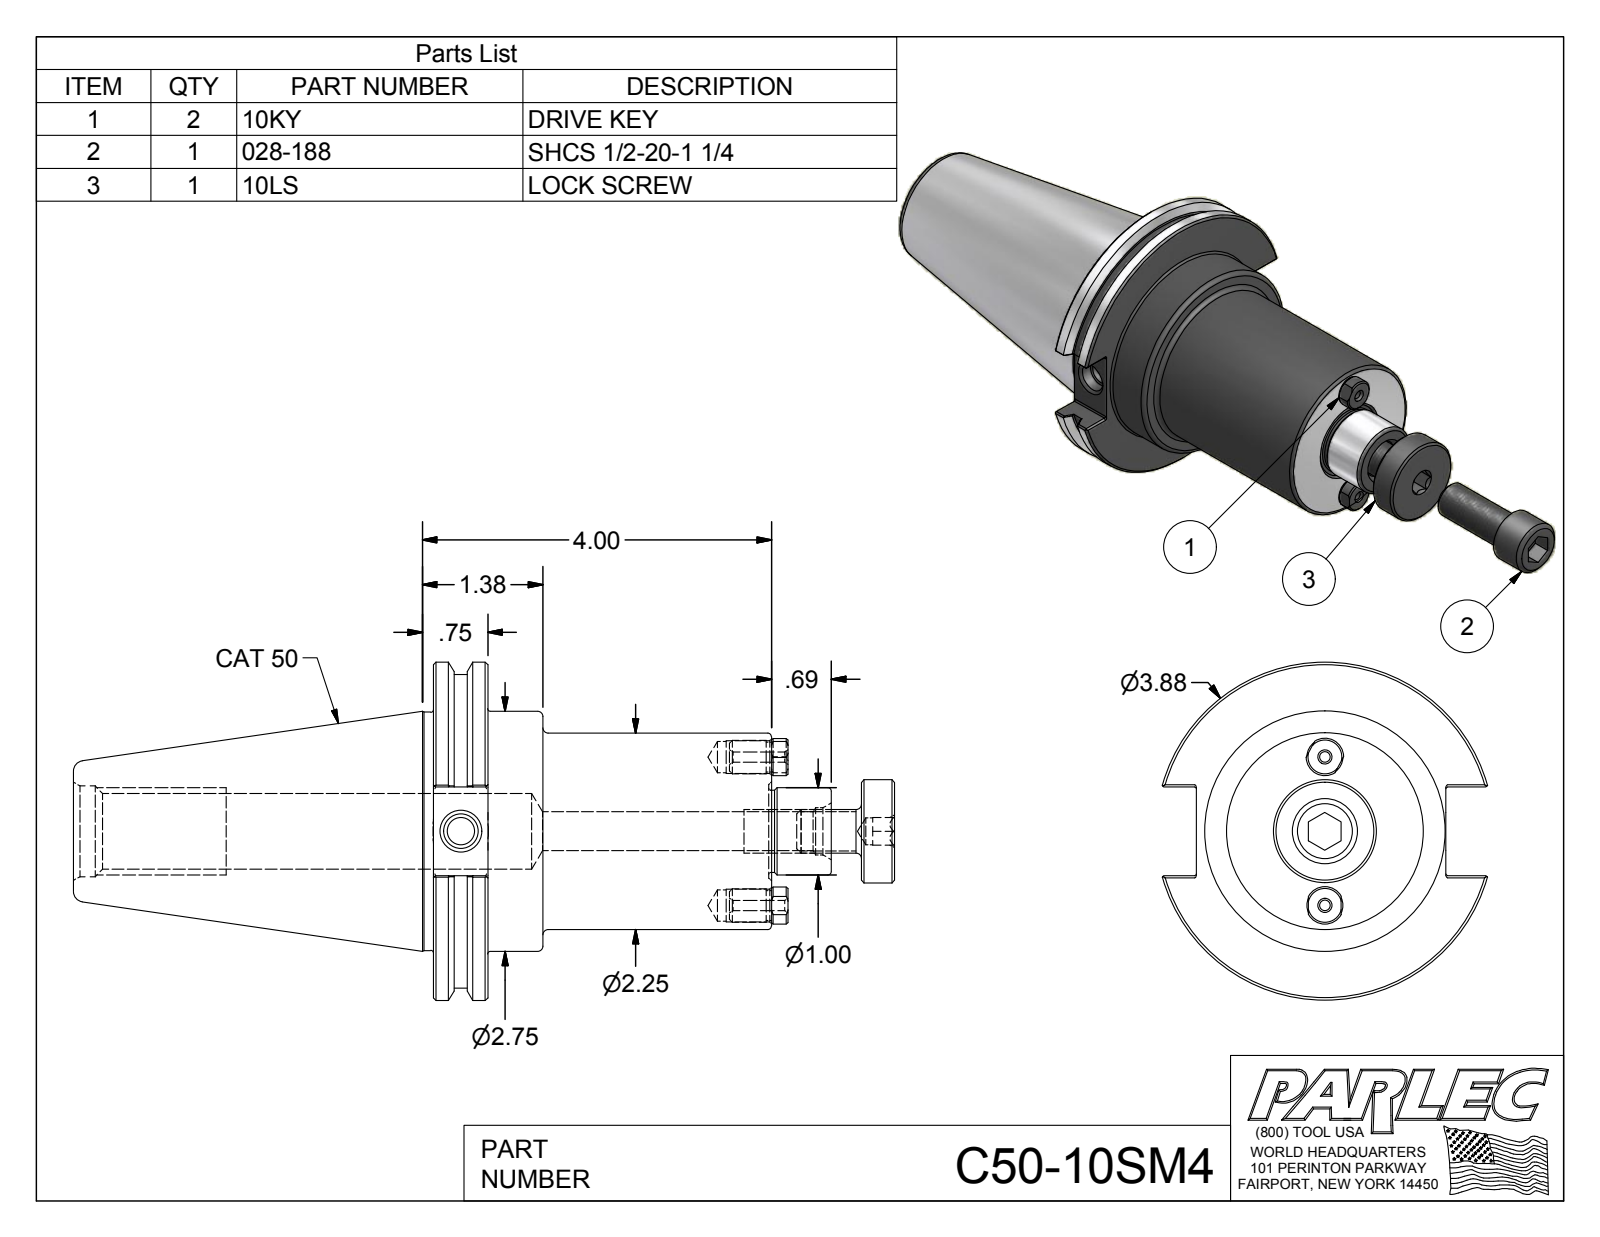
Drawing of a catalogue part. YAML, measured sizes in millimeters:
part_name: "C50-10SM4; C50-10SM4-1; 10KY; 028-188 (+1 more)"
step_written_by: "Autodesk Inventor 2012 (AUTOMOTIVE_DESIGN)"
units: millimeters
bodies: {solids: 5, faces: 177, planar: 68, cylindrical: 48, other: 61}
overall_size: [296.4, 98.4, 94.7]
volume: 559300
surface_area: 73350
round_holes:
  - {diameter: 3, count: 2}
  - {diameter: 9, count: 2}
  - {diameter: 9.5, count: 2}
  - {diameter: 7.9, count: 1}
  - {diameter: 8, count: 1}
  - {diameter: 10.1, count: 1}
  - {diameter: 11.3, count: 1}
  - {diameter: 13.7, count: 1}
  - {diameter: 22, count: 1}
  - {diameter: 26.4, count: 1}
round_bosses_or_shafts:
  - {diameter: 9.7, count: 2}
  - {diameter: 8.6, count: 2}
  - {diameter: 98.4, count: 1}
  - {diameter: 91.3, count: 1}
  - {diameter: 69.9, count: 1}
  - {diameter: 69.3, count: 1}
  - {diameter: 57.2, count: 1}
  - {diameter: 30, count: 1}
partial_cylinders:
  - {radius: 0.5, count: 12}
  - {radius: 5.4, count: 2}
face_to_face_distances: [15.9, 98.4, 82.6, 31.9, 16, 66.5, 134.2, 118.3, 102.3, 35.8]
hole_center_spacings: [21.6, 43.2]
